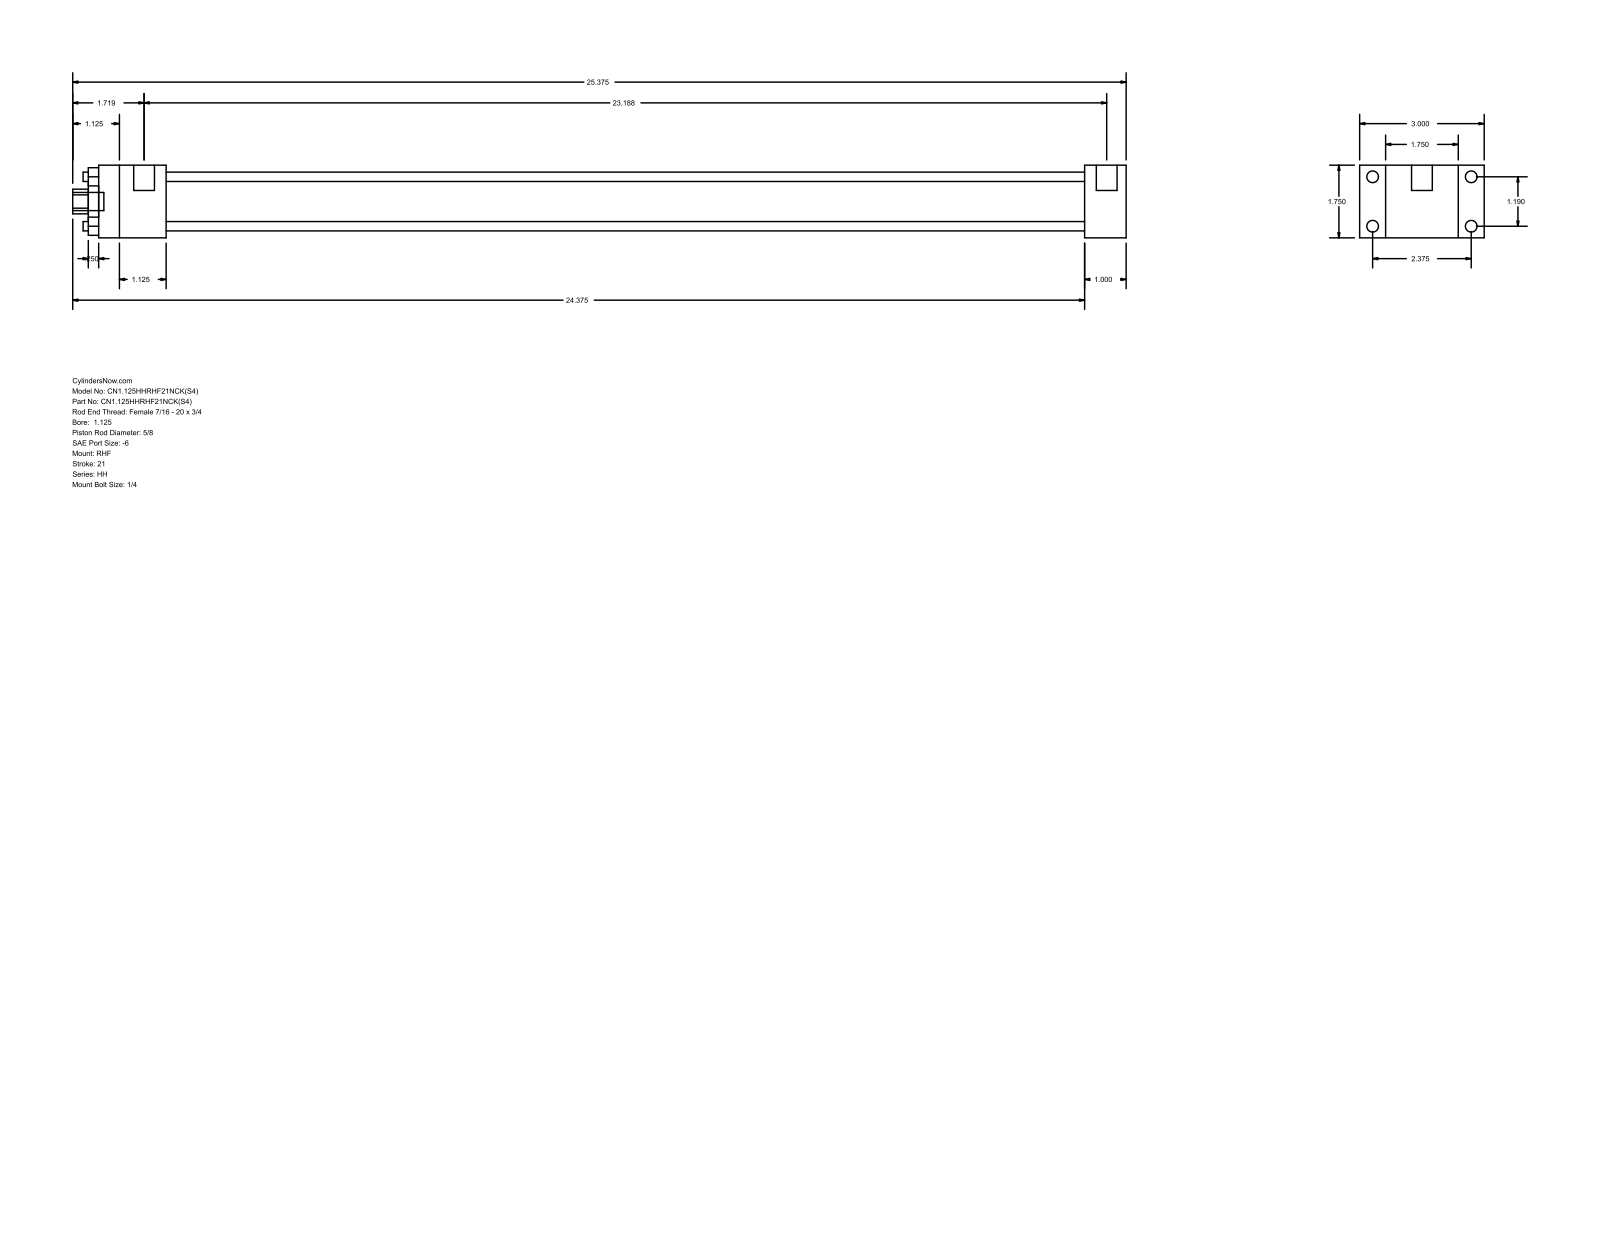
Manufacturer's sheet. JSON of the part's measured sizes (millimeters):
{"part_name": "HH_RHF__0112_0.625", "step_written_by": "GSSL Pune (CONFIG_CONTROL_DESIGN)", "units": "millimeters", "bodies": {"solids": 0, "faces": 88, "planar": 60, "cylindrical": 28, "other": 0}, "overall_size": [644.52, 76.2, 44.45], "round_holes": [[5.71, 4], [15.88, 1], [28.57, 1], [34.92, 1]], "round_bosses_or_shafts": [[7.14, 4], [5.56, 4], [12.7, 2], [11.11, 1]], "partial_cylinders_radius": [[7.54, 1]], "face_to_face_distances": [44.46, 15.87, 60.33, 25.4, 76.2, 561.97, 587.37, 41.27, 603.24, 628.64], "hole_center_spacings": [21.37, 30.22, 42.74]}
